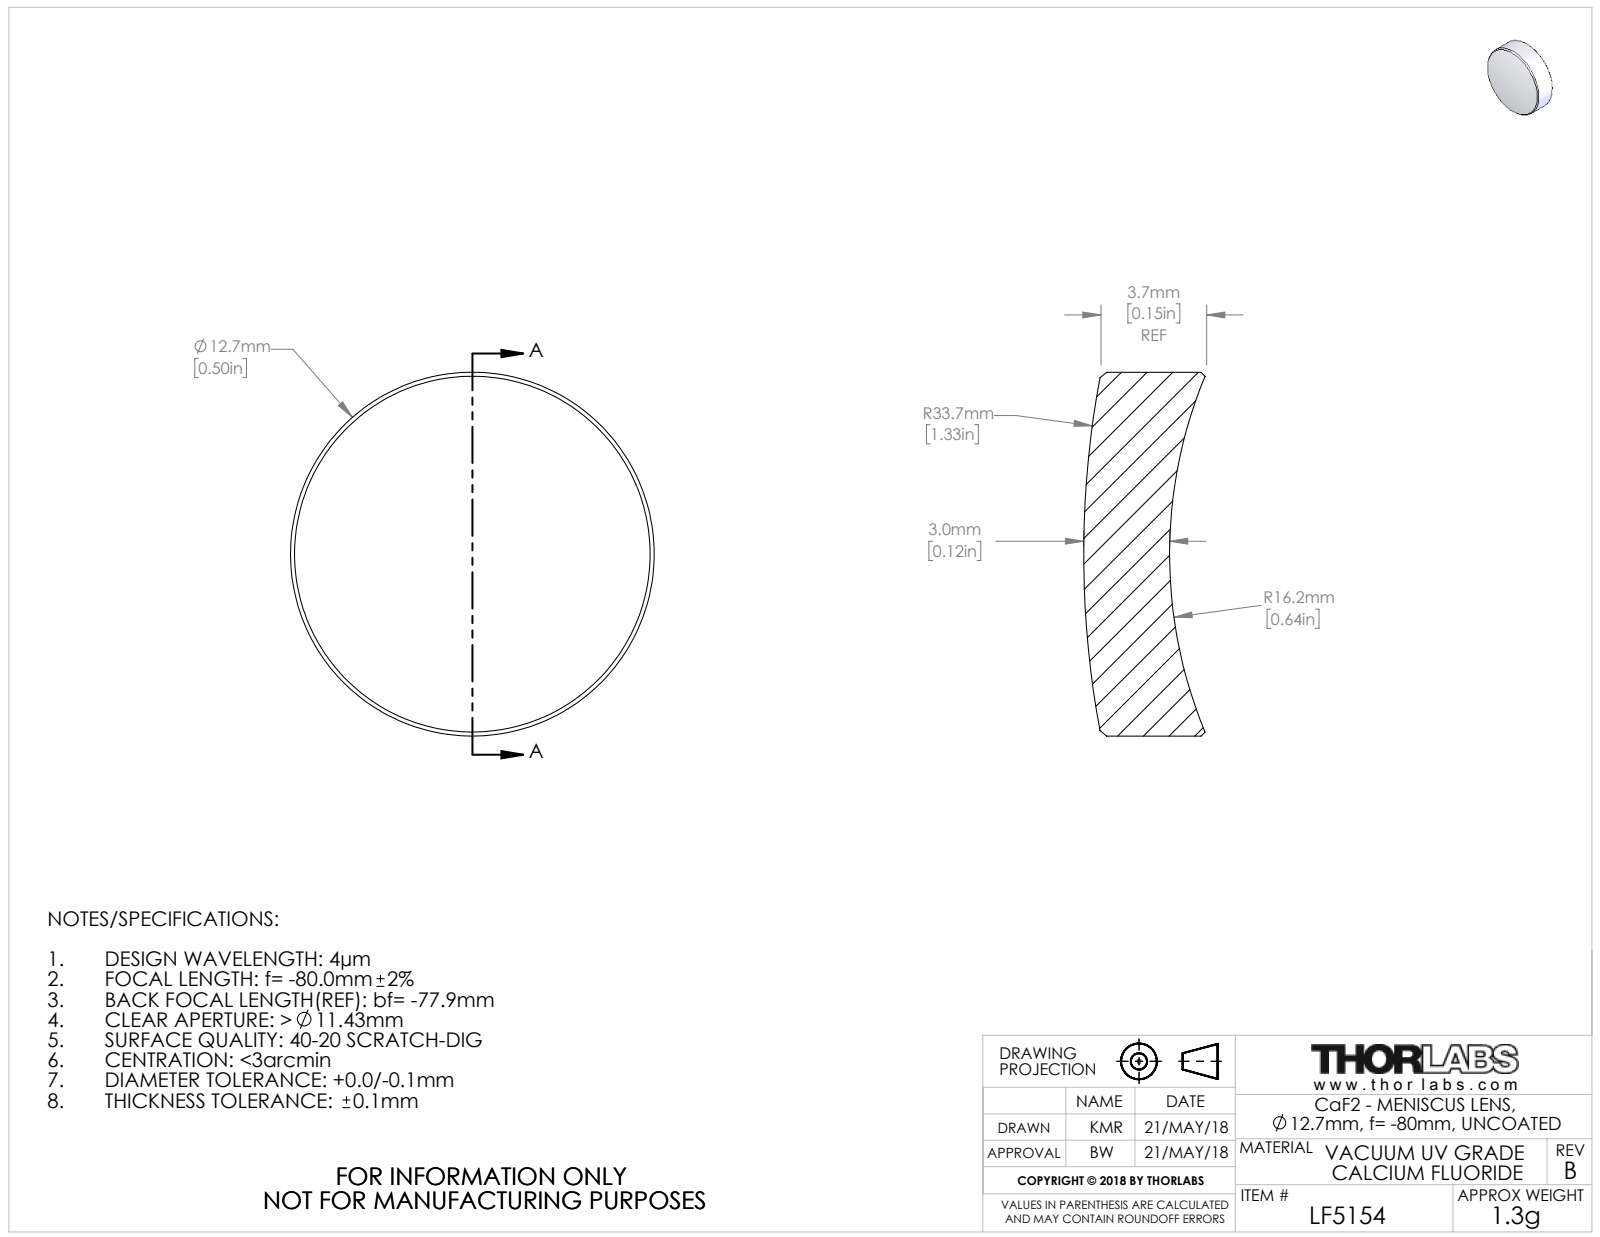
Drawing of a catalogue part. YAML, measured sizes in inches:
part_name: "21997-E0W"
step_written_by: "SolidWorks 2016 (CONFIG_CONTROL_DESIGN)"
units: inches
bodies: {solids: 1, faces: 10, planar: 0, cylindrical: 2, other: 8}
overall_size: [0.5, 0.5, 0.167]
volume: 0.026
surface_area: 0.616
round_bosses_or_shafts:
  - {diameter: 0.5, count: 1}
